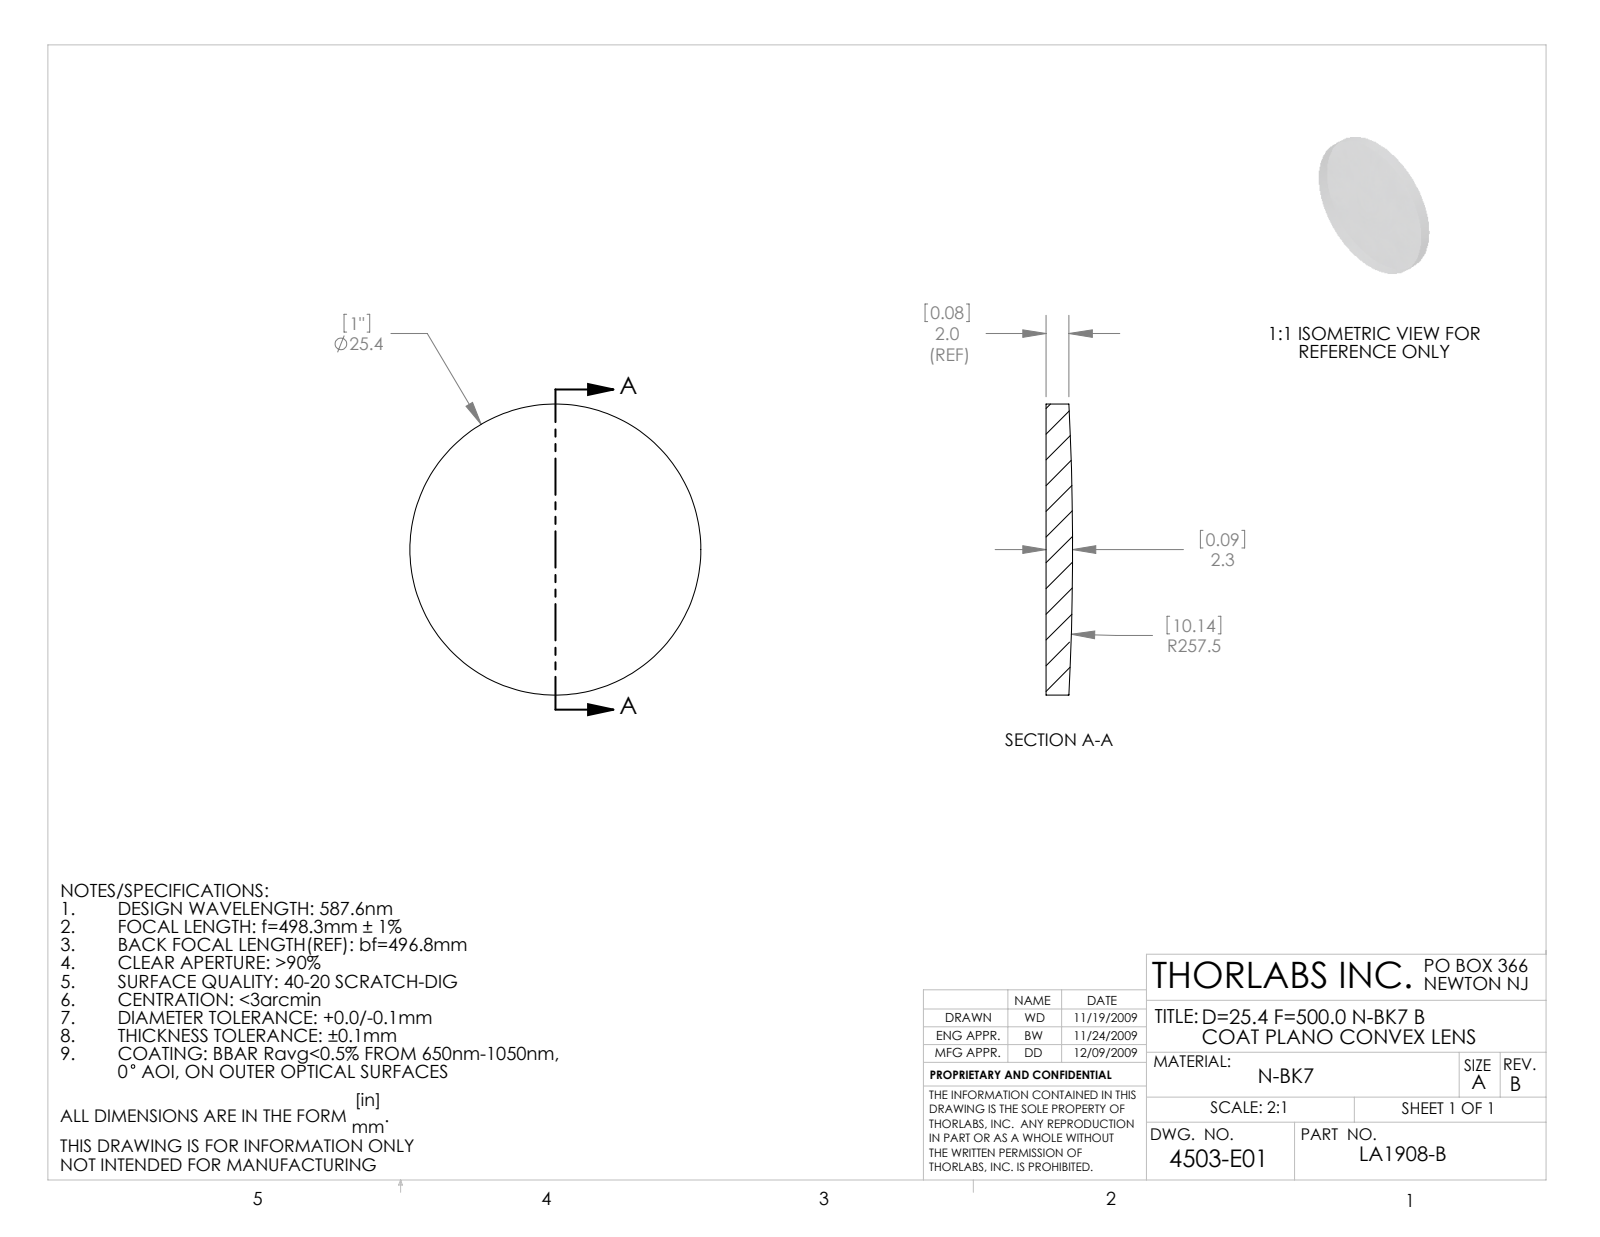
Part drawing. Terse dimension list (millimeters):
name: 4503-E0W
written by: SolidWorks 2009 (AUTOMOTIVE_DESIGN)
unit: mm
bodies: 1 solid, 5 faces (1 planar, 2 cylindrical, 2 other)
size: 25.4 × 25.4 × 2.31
volume: 1 091 mm³; area: 1 173 mm²
bosses: 1× ⌀25.4
